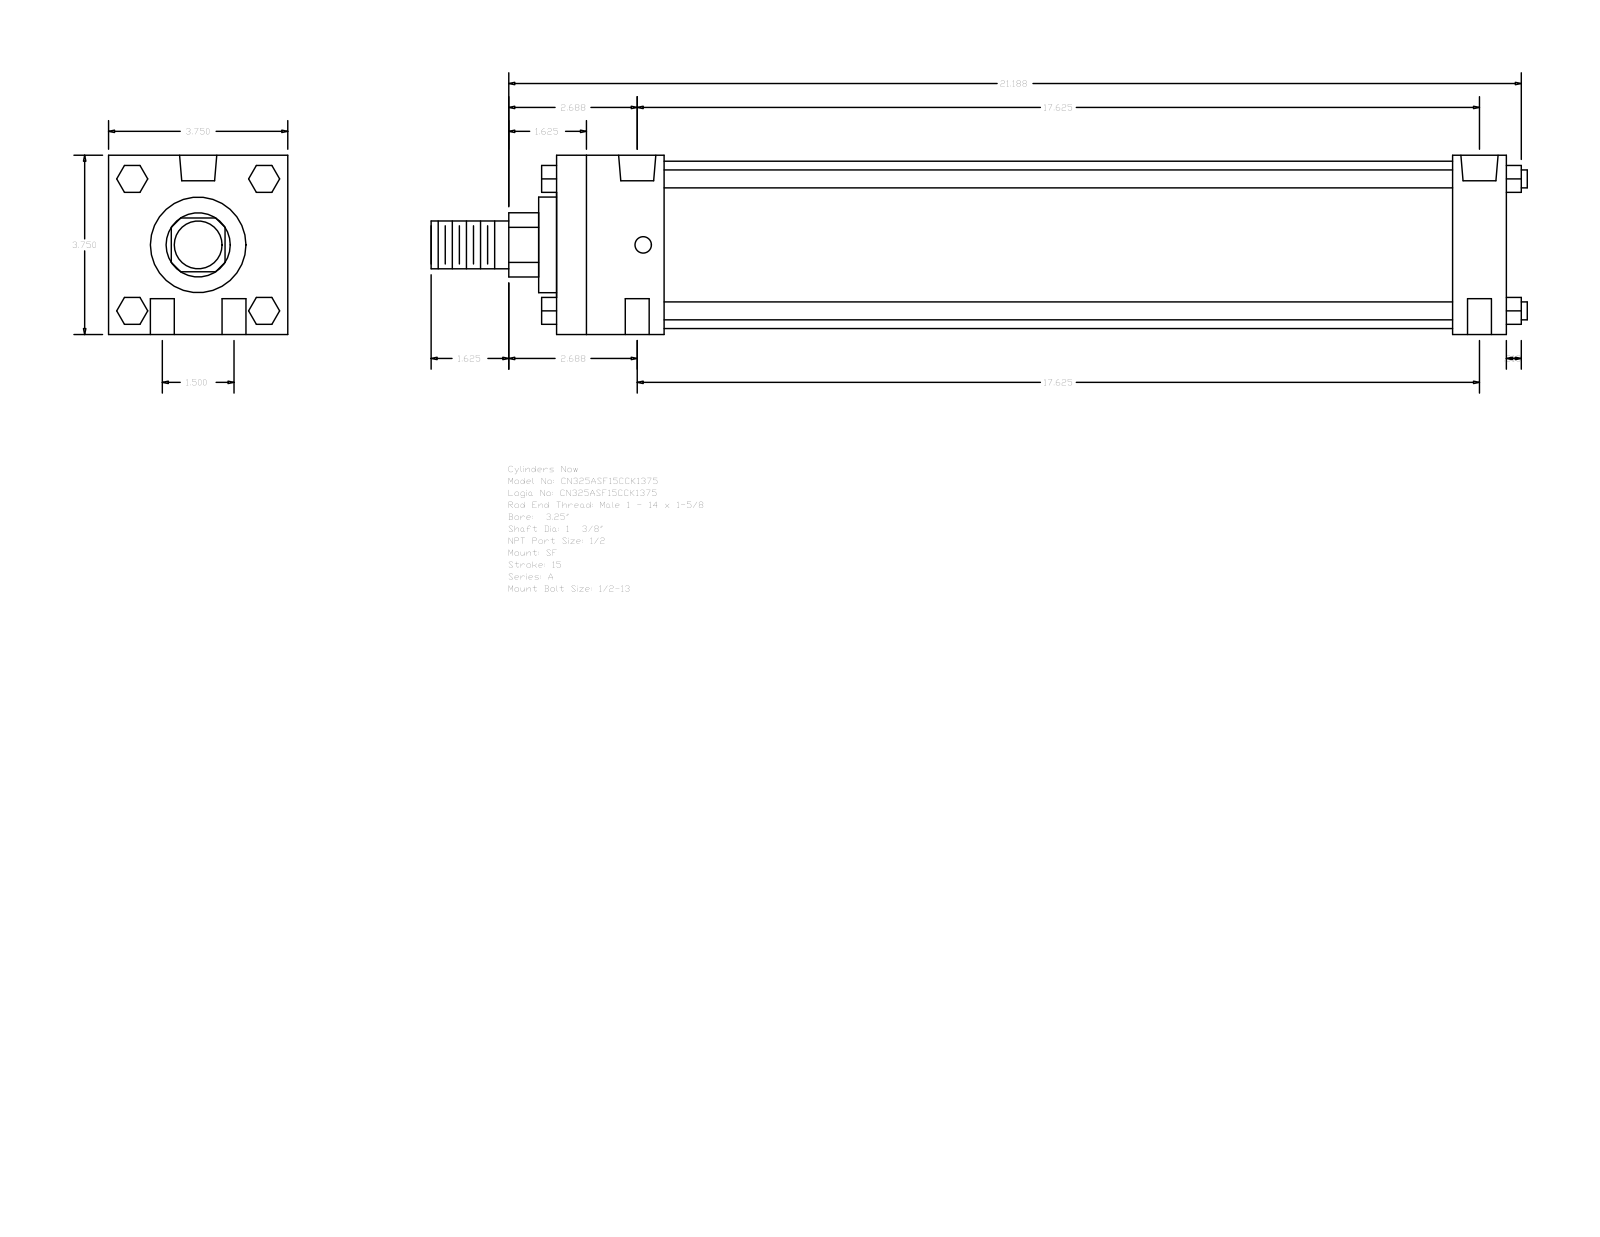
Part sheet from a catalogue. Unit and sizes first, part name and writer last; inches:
Units: inches
Overall size (bounding box): 22.937 × 3.75 × 3.75
Round holes (diameter × count): ⌀0.5 ×4, ⌀0.344 ×2, ⌀0.778 ×2
Round bosses / shafts (diameter × count): ⌀0.375 ×4, ⌀3.5 ×1, ⌀2 ×1, ⌀1.375 ×1, ⌀1 ×1
Partial cylindrical surfaces — rounded edges, fillets, slot ends (radius × count): R0.672 ×1
Main face-to-face distances: 3.75, 19.875, 2.25, 1.125, 18.75, 16.5, 17.625, 2.625, 0.375, 19.125
Hole centre spacings: 0.75, 17.641, 17.625, 1.5, 17.689, 17.375
Bodies: 0 solids, 124 faces (94 planar, 30 cylindrical, 0 other)
Part name (STEP PRODUCT): A_SF__0325_1.375
STEP written by: GSSL Pune (CONFIG_CONTROL_DESIGN)
